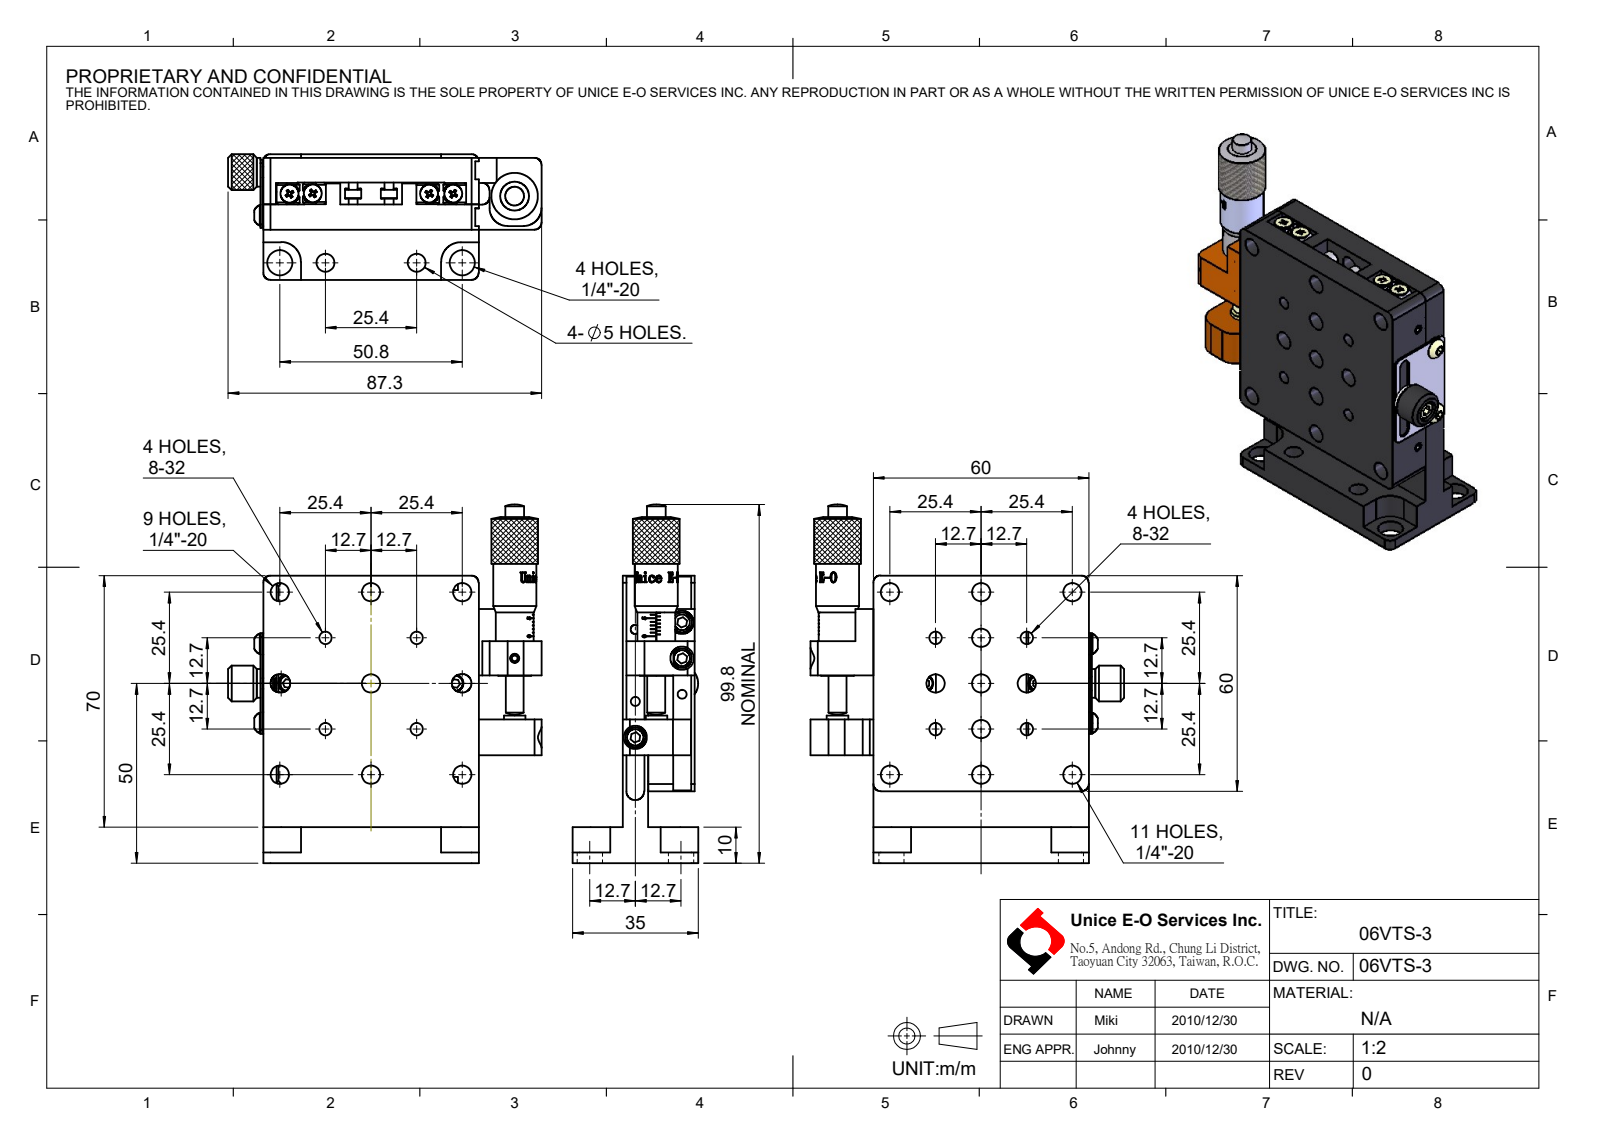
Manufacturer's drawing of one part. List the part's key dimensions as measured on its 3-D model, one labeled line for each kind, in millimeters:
Part name (STEP PRODUCT): 06VTS-3
STEP written by: SolidWorks 2016 (CONFIG_CONTROL_DESIGN)
Units: millimetres
Bodies: 50 solids, 1660 faces (843 planar, 429 cylindrical, 388 other)
Overall size (bounding box): 99.79 × 87.3 × 35
Volume: 91 418 mm³ · Surface area: 51 203 mm²
Round holes (diameter × count): ⌀2.05 ×20, ⌀5 ×17, ⌀2.5 ×15, ⌀3 ×13, ⌀5.11 ×11, ⌀3.45 ×4, ⌀7 ×4, ⌀3.4 ×3, ⌀6.5 ×3, ⌀3.2 ×2, ⌀3.5 ×2, ⌀6 ×2
Round bosses / shafts (diameter × count): ⌀4.5 ×16, ⌀2.5 ×16, ⌀3 ×9, ⌀5.5 ×4, ⌀5 ×4, ⌀2.55 ×4, ⌀6 ×2, ⌀5.7 ×2
Partial cylindrical surfaces — rounded edges, fillets, slot ends (radius × count): R2 ×12, R5 ×4, R5.5 ×4, R2.5 ×3, R1.75 ×2, R2.55 ×2, R5.98 ×1
Main face-to-face distances: 7, 13, 20, 6, 6.1, 6.9, 13.1, 10, 12.9, 5.9
Hole centre spacings: 28.4, 12.7, 25.4, 17.96, 20, 40.16, 45.79, 35.92
